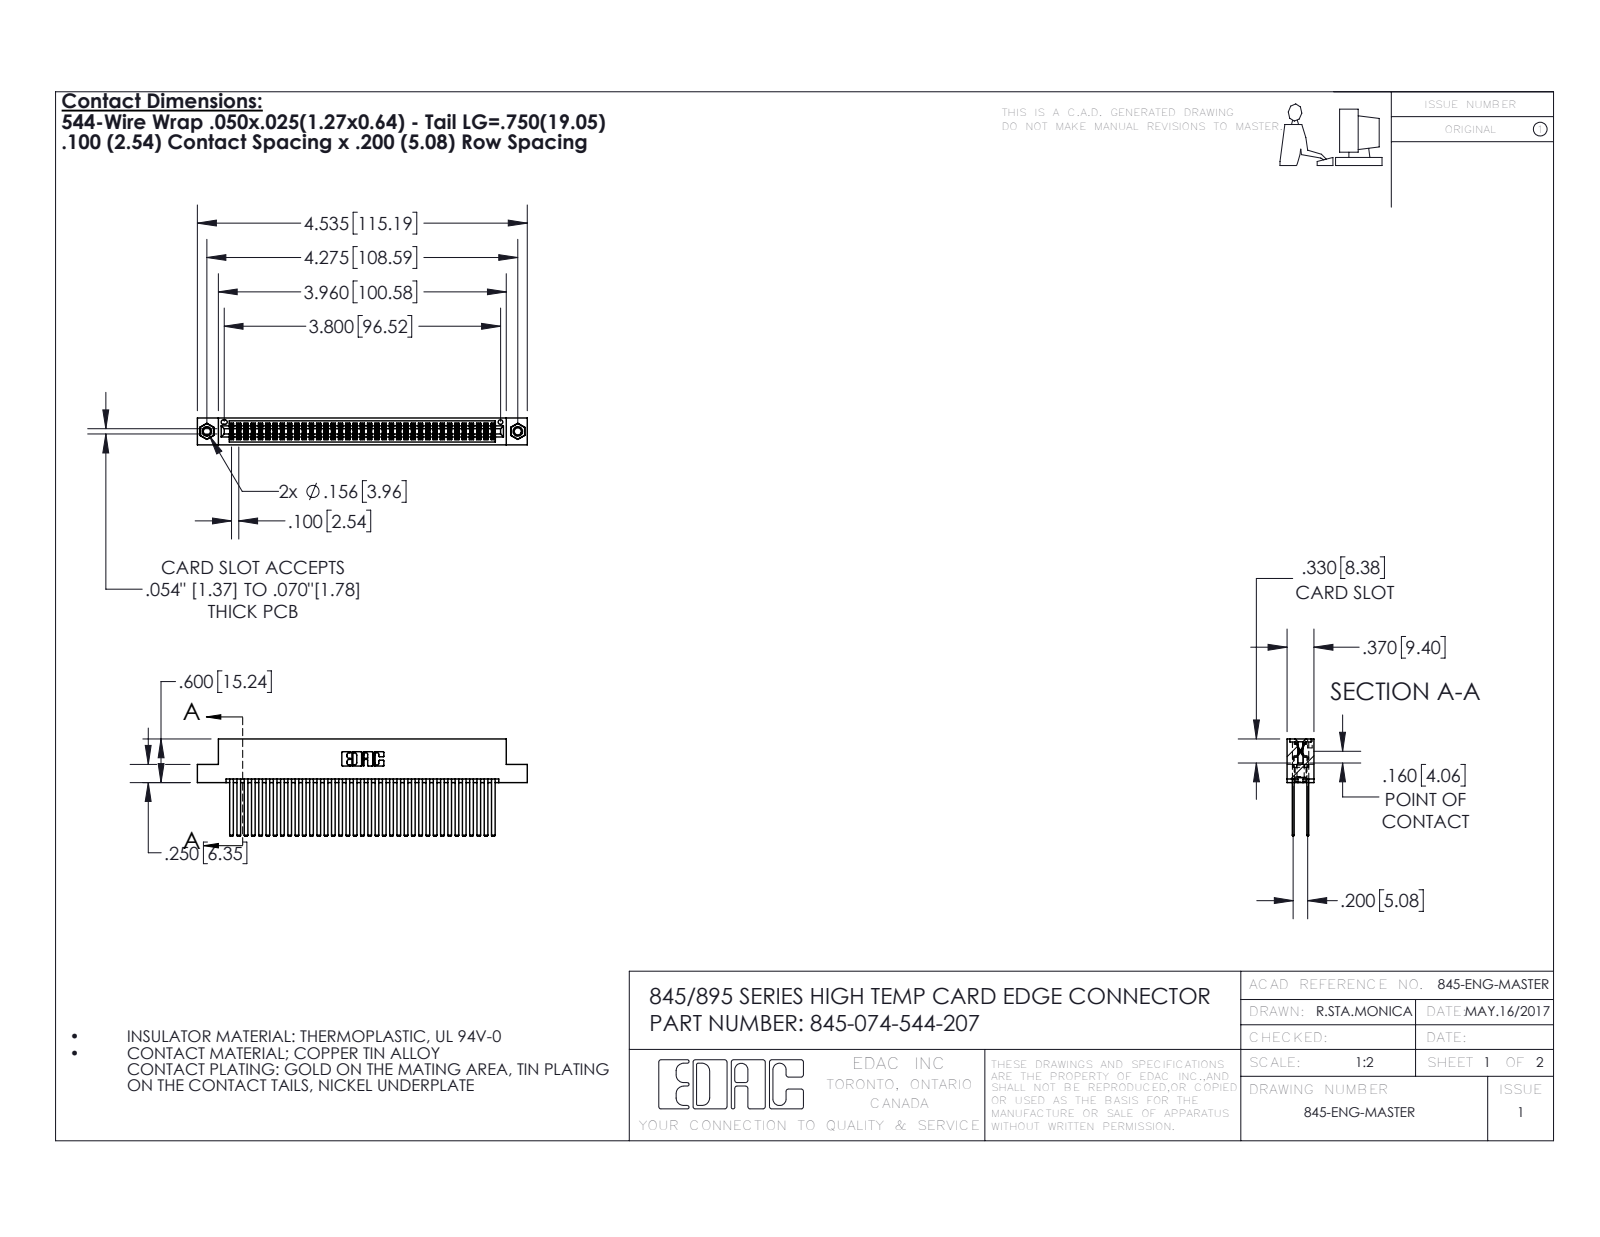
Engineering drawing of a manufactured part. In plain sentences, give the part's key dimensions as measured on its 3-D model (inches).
The part is named "345-074-544-207; 345 Part_Flush Mounting Lugs - 0.156 Dia-TI; 345-250-001_345-250-005-103; 345-292-001_345-293-144". Its 3-D file was written by "SolidWorks 2016 (CONFIG_CONTROL_DESIGN)". It is 77 solids with 3442 faces: 2258 planar, 1168 cylindrical and 16 other. Overall it measures 4.535 by 1.337 by 0.37 inches. Its volume is 0.742 cubic inches and its surface area 32.48 square inches. Round holes: 2 of diameter 0.098, 2 of diameter 0.125, 2 of diameter 0.156, 1 of diameter 0.064. Round bosses or shafts: 2 of diameter 0.155. Partial cylindrical surfaces (rounded edges, fillets, slot ends): 111 of radius 0.006, 22 of radius 0.01, 6 of radius 0.007, 6 of radius 0.031, 3 of radius 0.026, 2 of radius 0.014, 2 of radius 0.019, 2 of radius 0.022. The main face-to-face distances are 0.2, 0.025, 0.072, 0.098, 0.272, 0.298, 0.225, 0.175, 0.37, 0.05. The hole center spacings are 0.27, 4.039, 4.275.
